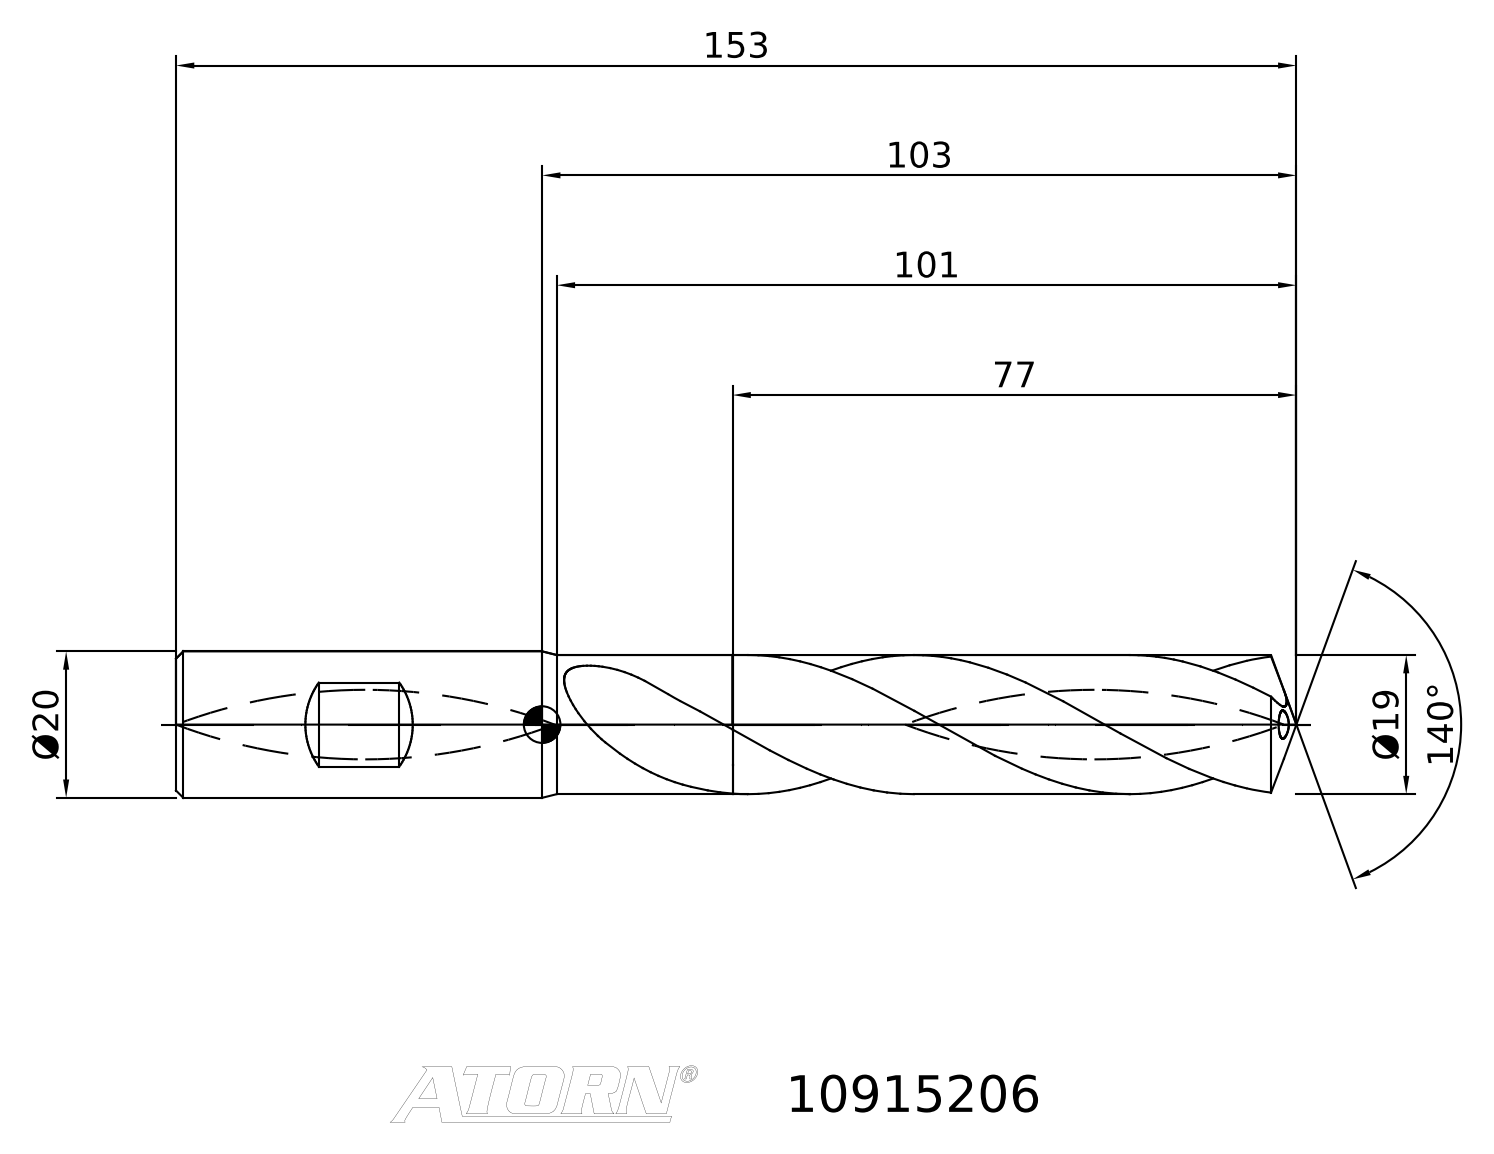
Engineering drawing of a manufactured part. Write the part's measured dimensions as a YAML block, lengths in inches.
step_written_by: "TDM (AUTOMOTIVE_DESIGN)"
units: inches
bodies: {solids: 2, faces: 33, planar: 8, cylindrical: 0, other: 25}
overall_size: [6.024, 1.176, 0.787]
volume: 2.145
surface_area: 16.29
face_to_face_distances: [2.992, 2.93, 5.922]
